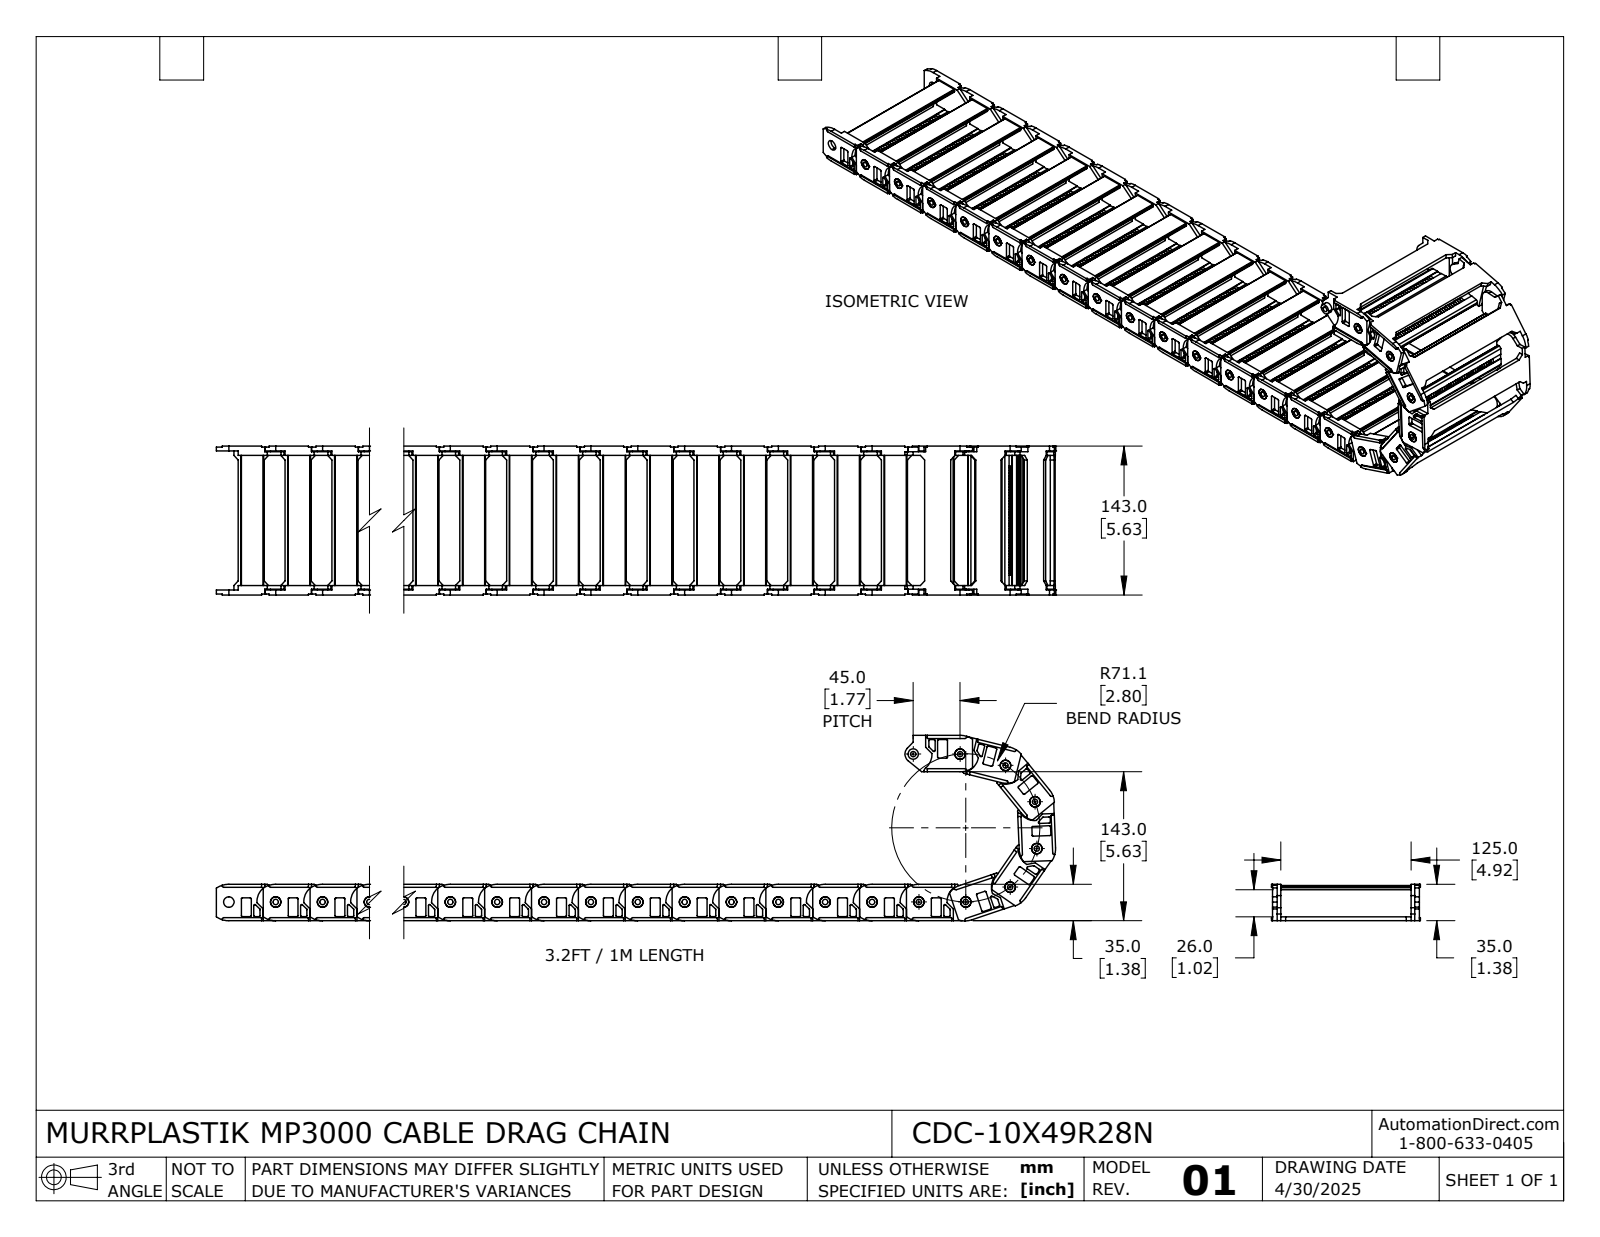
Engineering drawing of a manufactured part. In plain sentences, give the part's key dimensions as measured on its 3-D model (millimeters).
The part is named "CDC-10X49R28N". Its 3-D file was written by "SolidWorks 2024 (AUTOMOTIVE_DESIGN)". It is 22 solids with 6160 faces: 5060 planar, 1100 cylindrical and 0 other. Overall it measures 818.28 by 178.14 by 143 millimeters. Its volume is 913 059 cubic millimeters and its surface area 573 607 square millimeters. Round holes: 22 of diameter 5.1, 22 of diameter 10.1. Round bosses or shafts: 22 of diameter 10. Partial cylindrical surfaces (rounded edges, fillets, slot ends): 176 of radius 1, 88 of radius 0.5, 44 of radius 1.5, 44 of radius 2, 44 of radius 21, 22 of radius 2.8, 22 of radius 8, 22 of radius 18. The main face-to-face distances are 4, 133, 3.8, 30, 33.8, 8, 26, 29.8, 3.7, 137.3. The hole center spacings are 45, 90, 135, 180, 225, 270, 315, 360.
